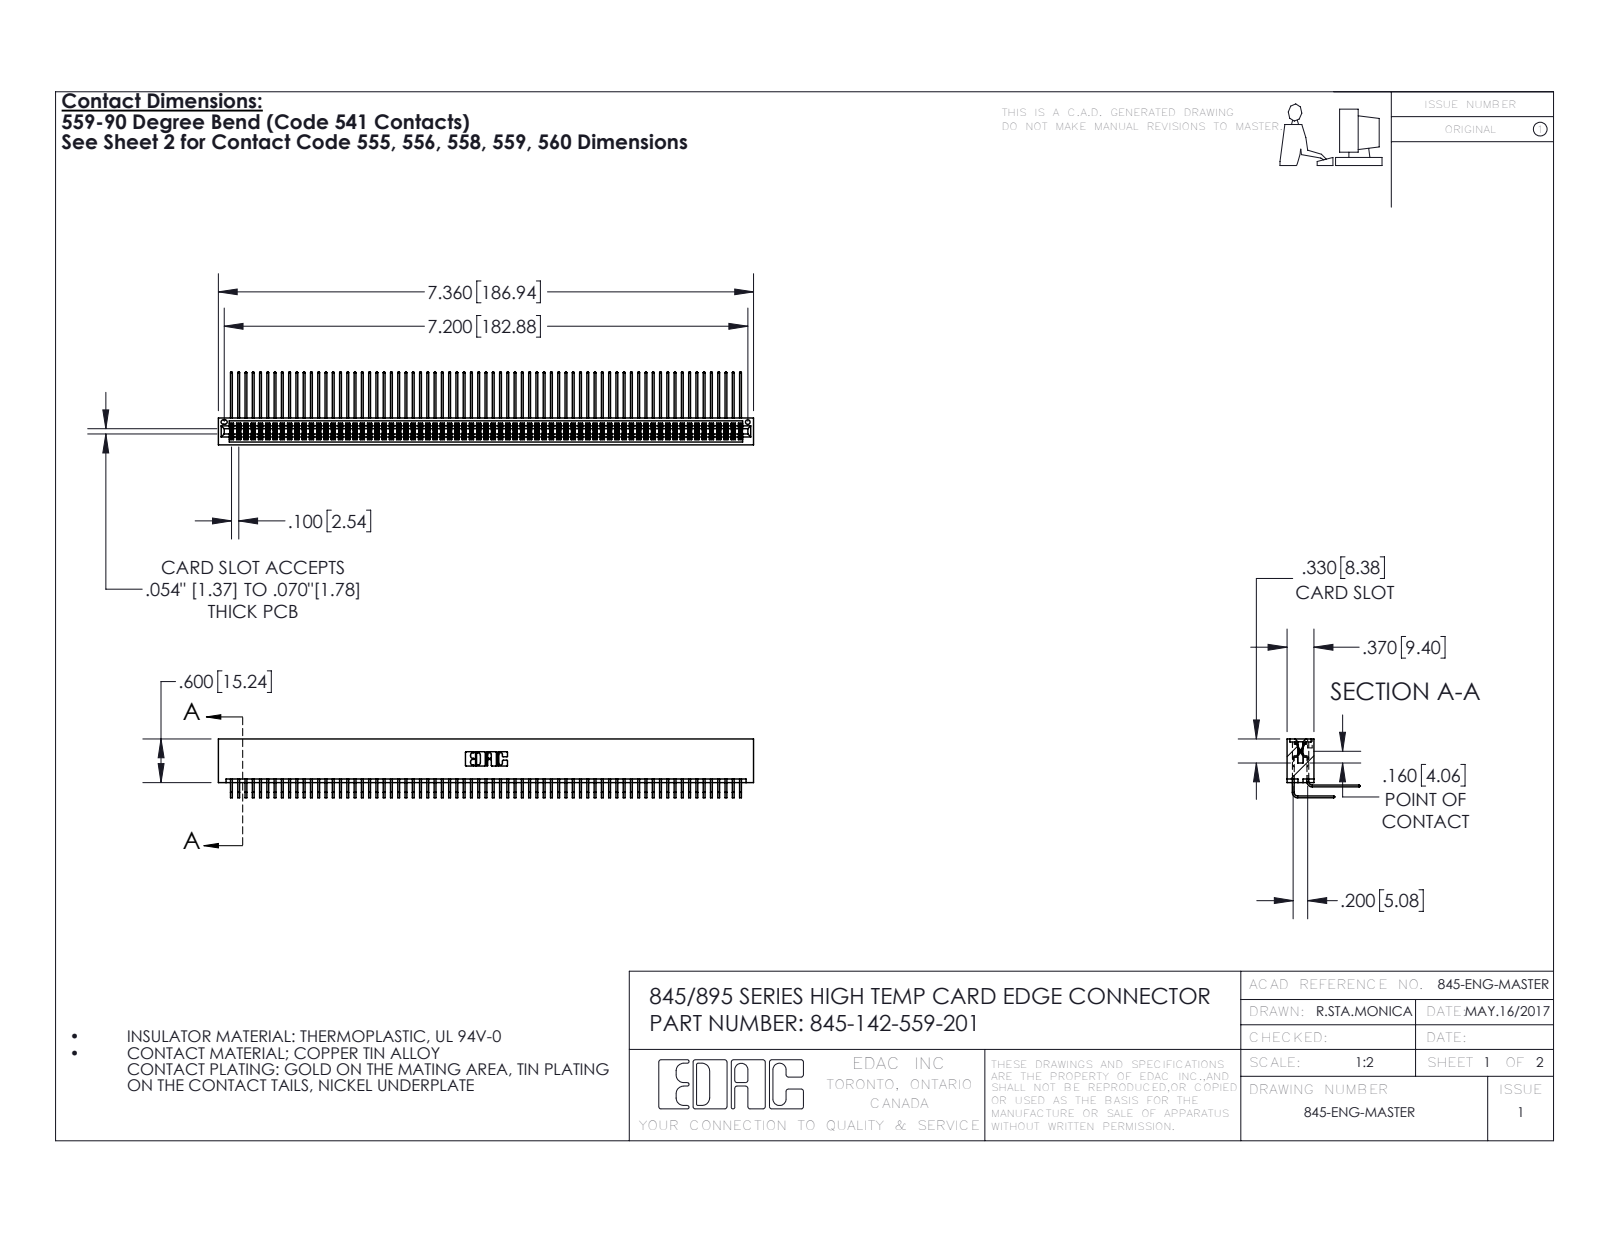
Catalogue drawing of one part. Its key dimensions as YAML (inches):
part_name: "345-292-001_558 559 Tail - 1; 345-142-559-201; 345-292-001_559 Tail - 2; 345 Part_No Mounting Lugs"
step_written_by: "SolidWorks 2016 (CONFIG_CONTROL_DESIGN)"
units: inches
bodies: {solids: 143, faces: 7502, planar: 5046, cylindrical: 2456, other: 0}
overall_size: [7.36, 1.005, 0.809]
volume: 1.212
surface_area: 52.82
round_holes:
  - {diameter: 0.064, count: 1}
partial_cylinders:
  - {radius: 0.006, count: 213}
  - {radius: 0.01, count: 22}
  - {radius: 0.007, count: 6}
  - {radius: 0.031, count: 6}
  - {radius: 0.026, count: 3}
  - {radius: 0.014, count: 2}
  - {radius: 0.019, count: 2}
  - {radius: 0.022, count: 2}
face_to_face_distances: [0.072, 0.298, 0.2, 0.37, 0.098, 0.272, 0.025, 0.225, 0.175, 0.15]
